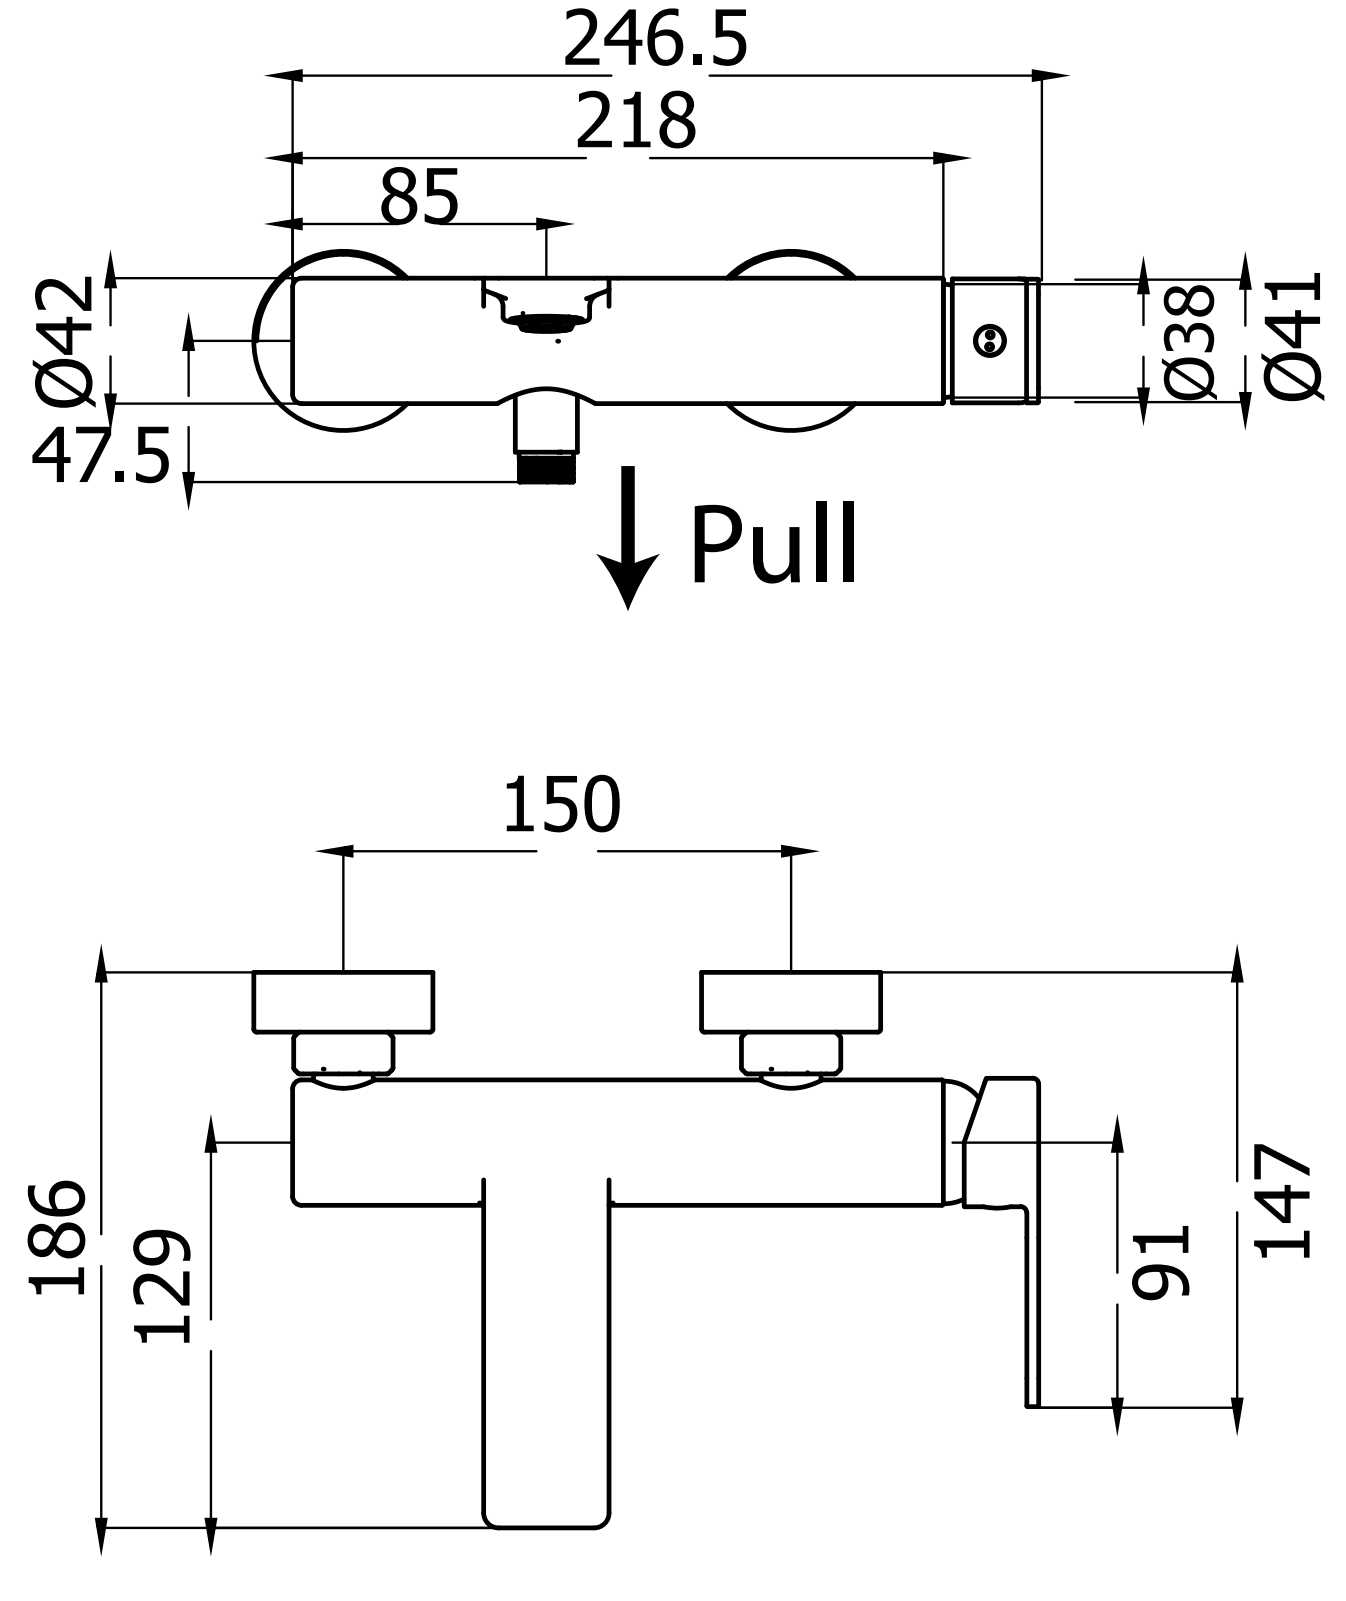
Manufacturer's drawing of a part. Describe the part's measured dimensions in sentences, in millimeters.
The part is named "AOTT005C002; SPLMAC0001; ott1111.stp; TOM2C788654AYIV_1 (+8 more)". Its 3-D file was written by "Shapr3D (AUTOMOTIVE_DESIGN)". It is 14 solids with 3283 faces: 1991 planar, 736 cylindrical and 556 other. Overall it measures 257.83 by 186 by 77.27 millimeters. Its volume is 171 167 cubic millimeters and its surface area 163 258 square millimeters. Round holes: 317 of diameter 0.5, 3 of diameter 19, 3 of diameter 21, 2 of diameter 5.2, 2 of diameter 6, 2 of diameter 7, 2 of diameter 9, 2 of diameter 16.8, 2 of diameter 18.7, 2 of diameter 21.3, 2 of diameter 24, 2 of diameter 24.7. Round bosses or shafts: 3 of diameter 30, 2 of diameter 60, 2 of diameter 25, 2 of diameter 23.2, 2 of diameter 20, 2 of diameter 18, 2 of diameter 16.5, 2 of diameter 16. Partial cylindrical surfaces (rounded edges, fillets, slot ends): 40 of radius 0.5, 24 of radius 0.8, 22 of radius 3.7, 7 of radius 1, 6 of radius 1.6, 4 of radius 1.8, 4 of radius 2.5, 3 of radius 2.8. The main face-to-face distances are 2.2, 1, 4, 2, 15, 38.1, 35.9, 19.9, 39.1, 36.9. The hole center spacings are 7.69, 7.7, 6.99, 0.88, 1.61, 3.2, 7, 6.26.
